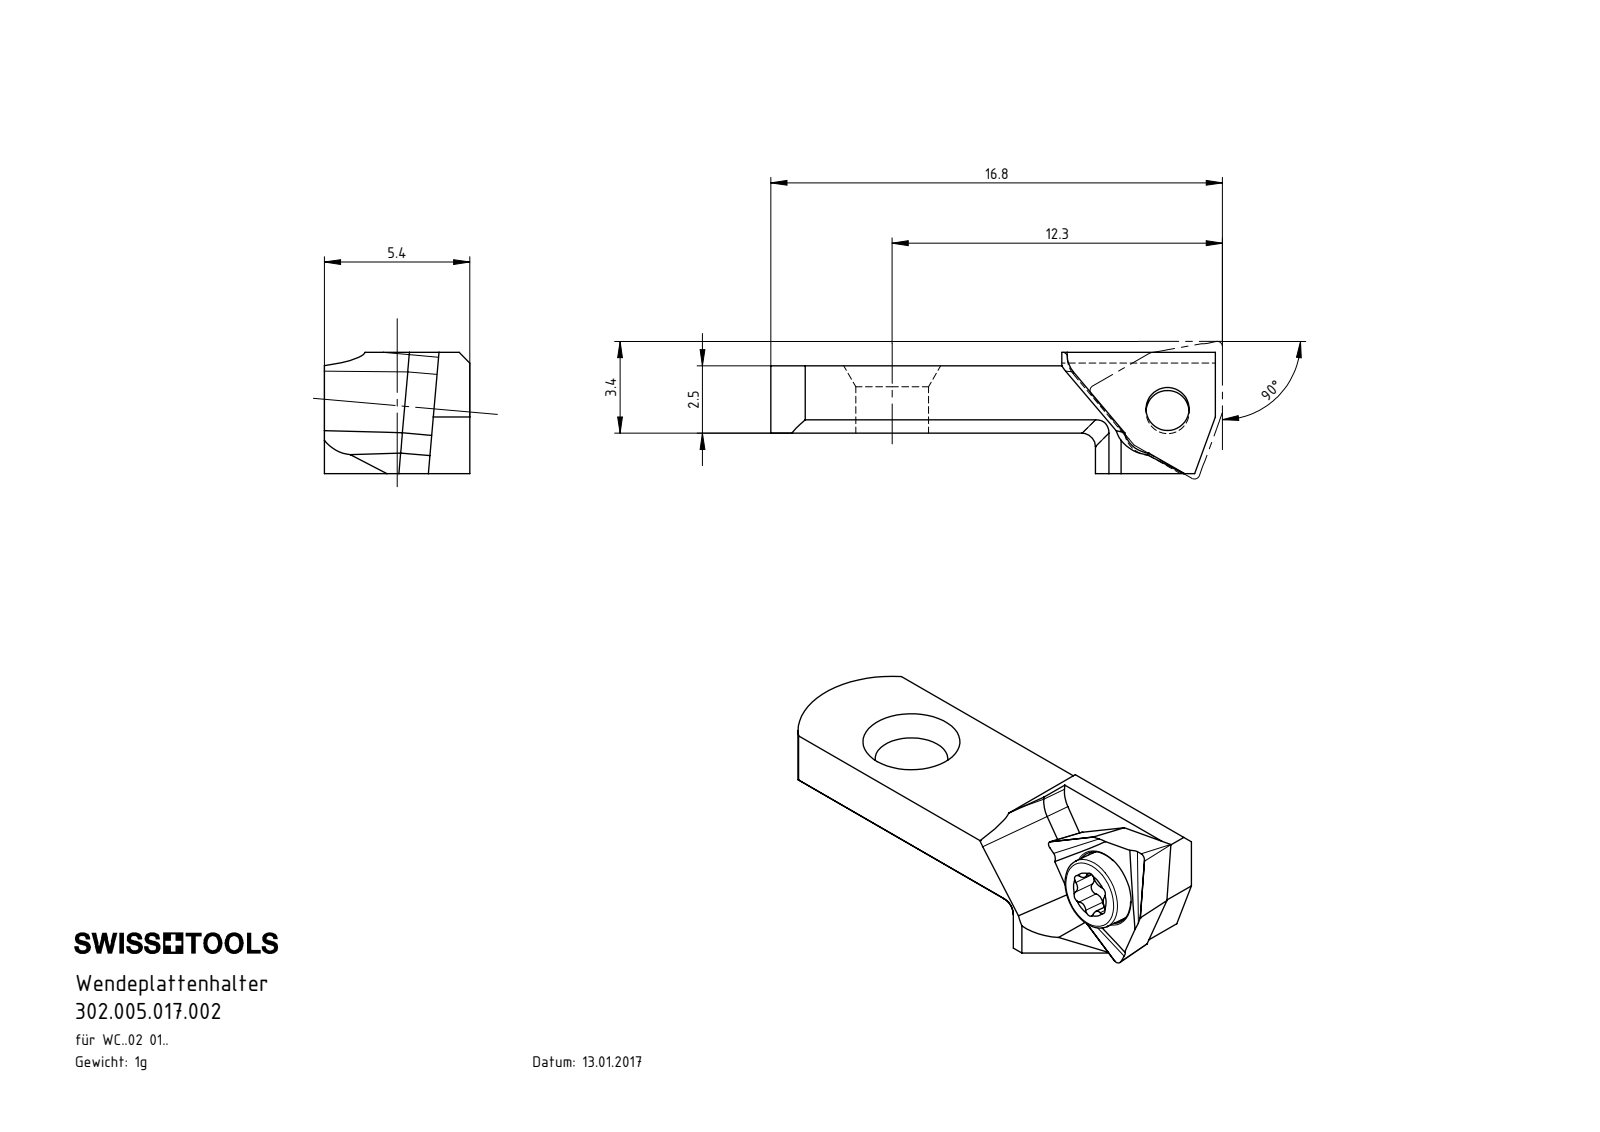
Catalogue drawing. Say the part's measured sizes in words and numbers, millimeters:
The part is named "WWA-SFH.020.004; 302.005.017.002; WWA-ER2.001.004_A; F14-WWA.001.004_C". Its 3-D file was written by "SolidWorks 2017 (CONFIG_CONTROL_DESIGN)". It is 3 solids with 100 faces: 40 planar, 34 cylindrical and 26 other. Overall it measures 16.76 by 5.59 by 5.11 millimeters. Its volume is 200 cubic millimeters and its surface area 387 square millimeters. Round holes: 1 of diameter 1.6, 1 of diameter 2.3, 1 of diameter 2.7. Round bosses or shafts: 1 of diameter 2.7, 1 of diameter 2. Partial cylindrical surfaces (rounded edges, fillets, slot ends): 6 of radius 0.17, 6 of radius 0.32, 3 of radius 0.3, 2 of radius 0.7, 2 of radius 1, 1 of radius 0.5, 1 of radius 3.5. The main face-to-face distances are 2.5, 5.4, 1.5, 4, 4.5, 3, 0.5, 1.59, 5.3, 2.24.
